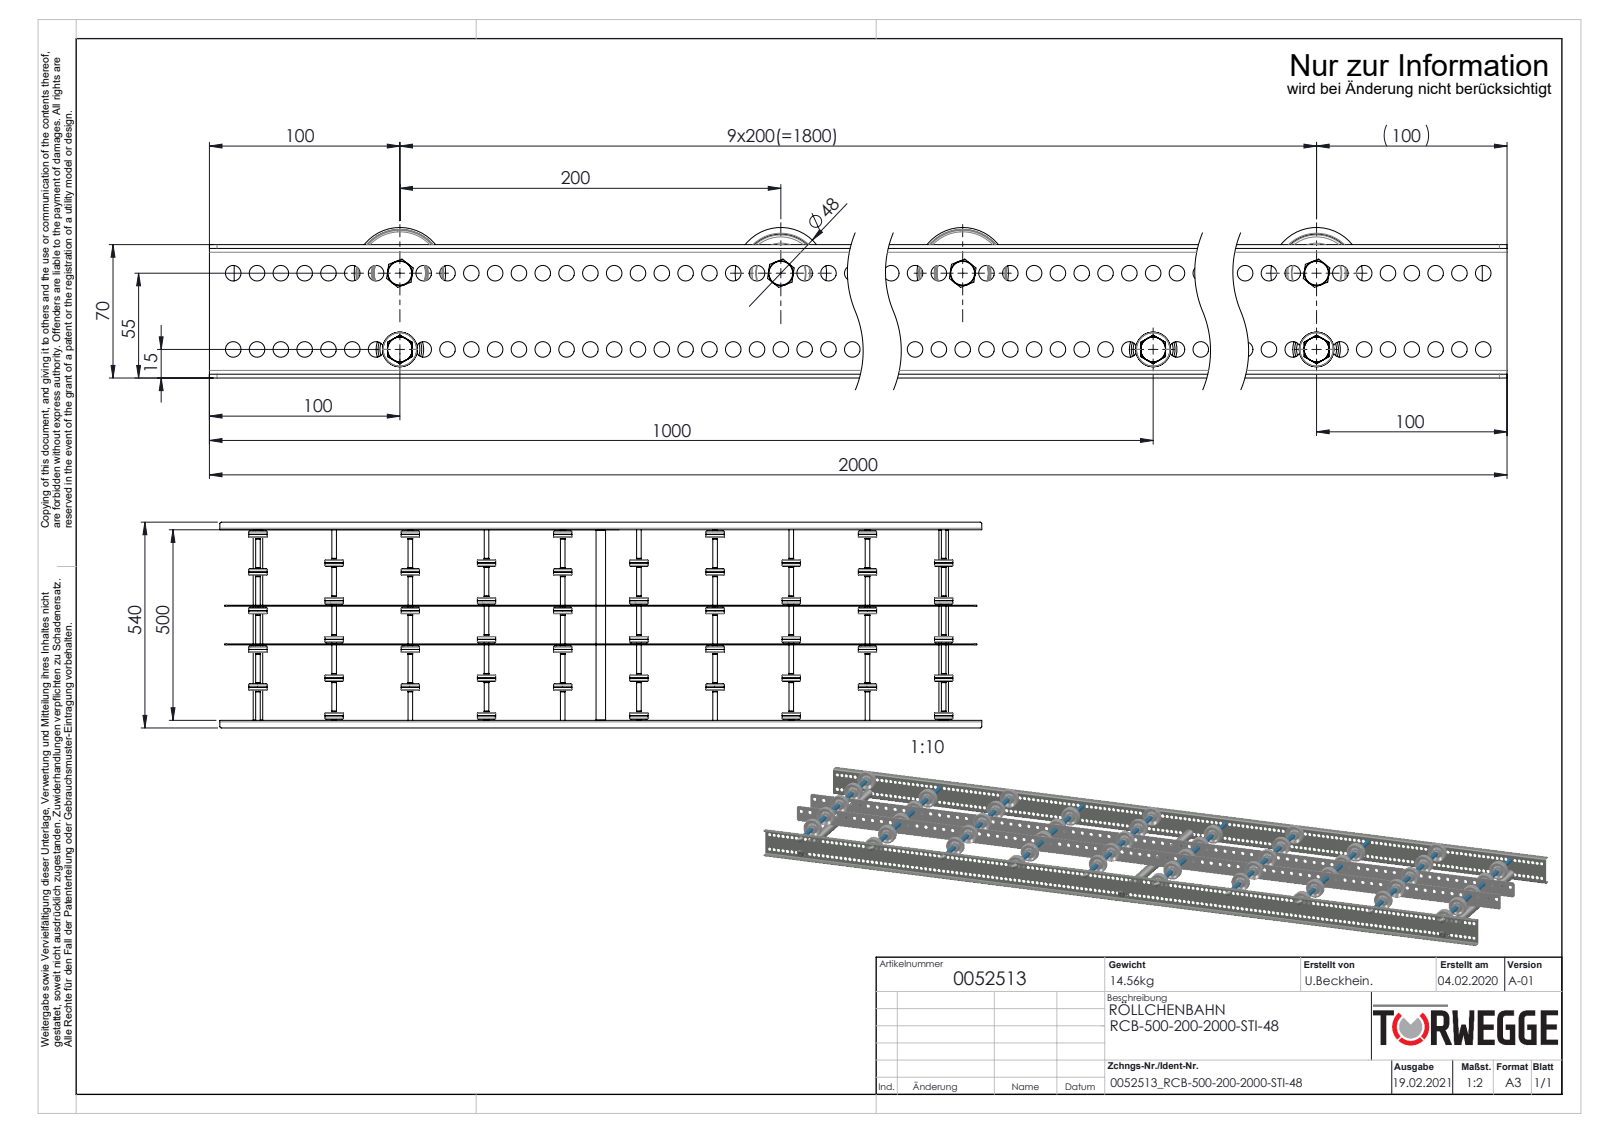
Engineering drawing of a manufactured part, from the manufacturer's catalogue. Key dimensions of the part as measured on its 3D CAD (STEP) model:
Part name (STEP PRODUCT): S100100_Längstraverse-42x2,5_S100103_Lngstraverse-RB-L2000; S100994_Sperrzahnschraube_M08x16-8.8-A2K; 0052513; K0011528_2200-48-8 (+6 more)
STEP written by: SolidWorks 2020 (AUTOMOTIVE_DESIGN)
Units: millimetres
Bodies: 199 solids, 6942 faces (1254 planar, 3272 cylindrical, 2416 other)
Overall size (bounding box): 2000 × 540 × 79
Volume: 2 889 000 mm³ · Surface area: 2 410 000 mm²
Round holes (diameter × count): ⌀8.2 ×318, ⌀8.5 ×79, ⌀6.65 ×10, ⌀8 ×10, ⌀9.65 ×10, ⌀15 ×10, ⌀41 ×10, ⌀6.8 ×3, ⌀21 ×3
Round bosses / shafts (diameter × count): ⌀48 ×10, ⌀13 ×10, ⌀12.5 ×10, ⌀12.4 ×10, ⌀12 ×10, ⌀11.5 ×10, ⌀25 ×3, ⌀8 ×3
Partial cylindrical surfaces — rounded edges, fillets, slot ends (radius × count): R4 ×8, R2 ×4, R5 ×4
Main face-to-face distances: 2, 200.5, 302, 101.5, 502, 200, 202.5, 301.5, 304, 198
Hole centre spacings: 12.5, 25, 37.5, 50, 62.5, 75, 87.5, 100
